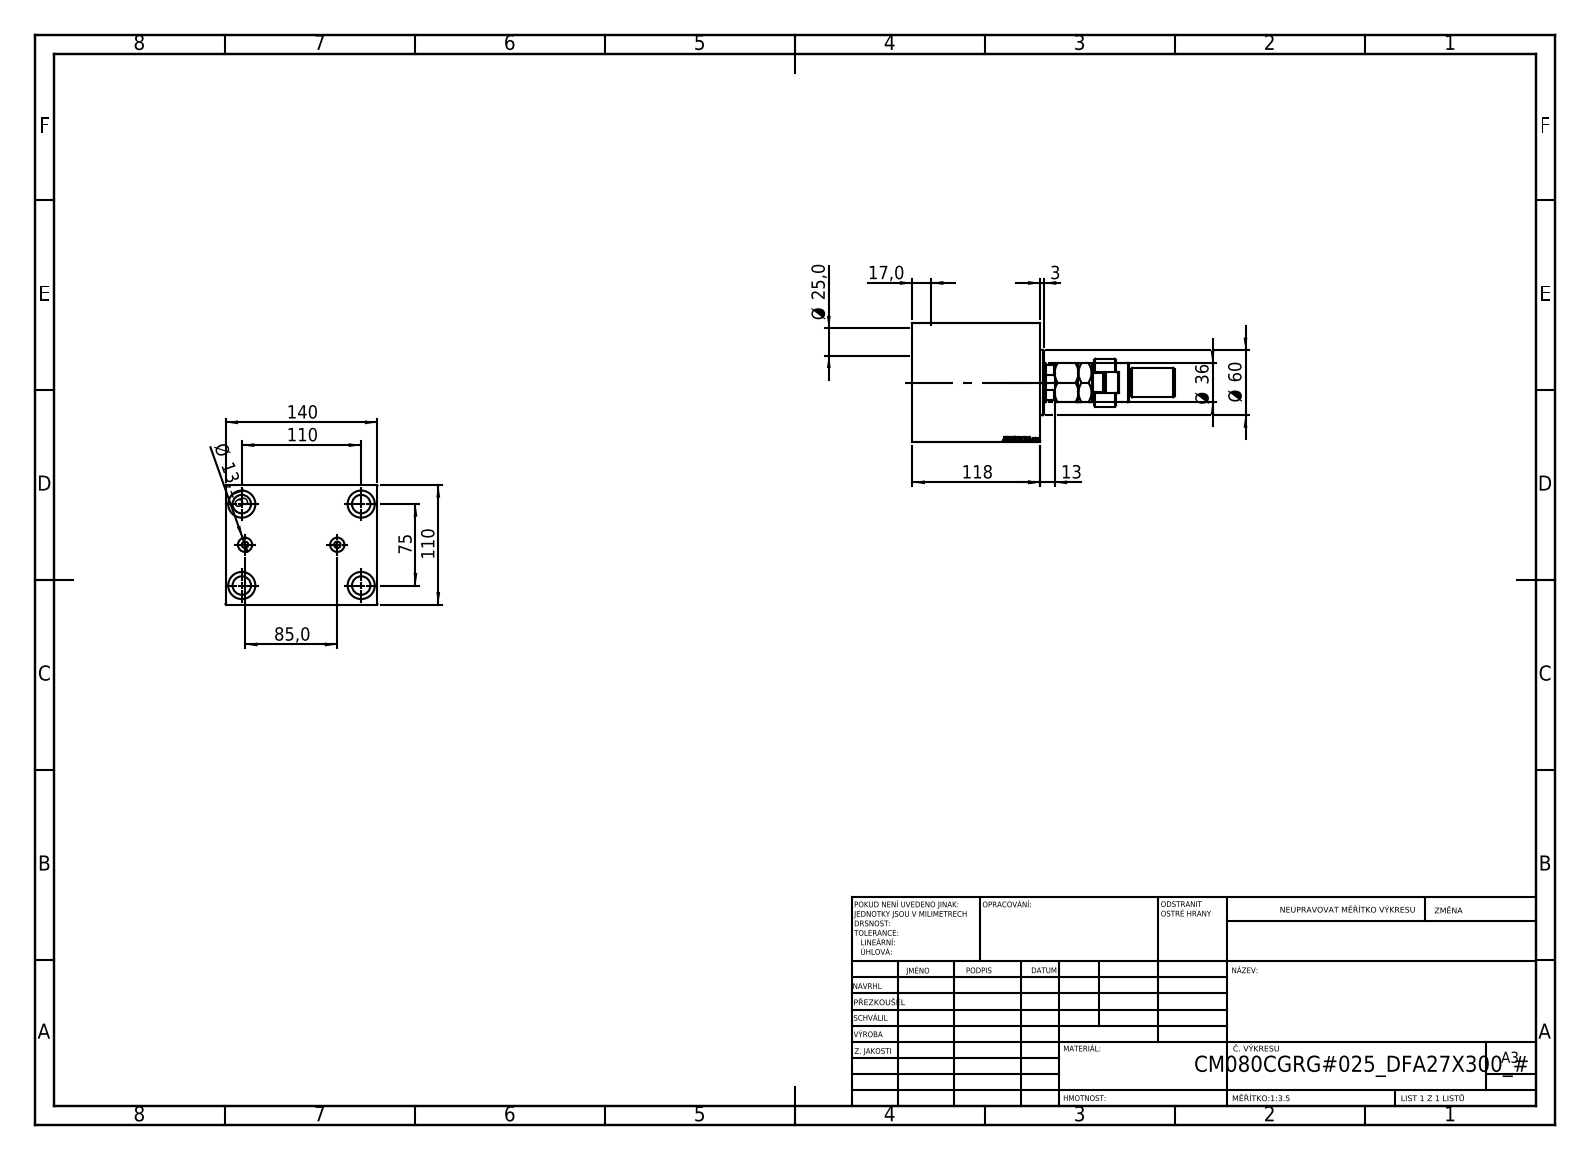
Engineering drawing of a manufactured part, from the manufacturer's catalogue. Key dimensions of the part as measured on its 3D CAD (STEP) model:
Part name (STEP PRODUCT): V450CM_C_Body; V450CM_VC_B; FEMALE_PART_FOR_DFA; MFA (+1 more)
STEP written by: SolidWorks 2019 (CONFIG_CONTROL_DESIGN)
Units: millimetres
Bodies: 5 solids, 945 faces (436 planar, 71 cylindrical, 438 other)
Overall size (bounding box): 241.5 × 140 × 110
Volume: 1 725 000 mm³ · Surface area: 195 676 mm²
Round holes (diameter × count): ⌀17 ×4, ⌀25 ×4, ⌀6 ×2, ⌀13.16 ×2, ⌀25.5 ×1, ⌀39.5 ×1, ⌀80 ×1, ⌀82 ×1, ⌀87 ×1
Round bosses / shafts (diameter × count): ⌀60 ×1, ⌀44 ×1, ⌀36 ×1, ⌀28 ×1, ⌀27 ×1, ⌀25 ×1, ⌀18 ×1
Partial cylindrical surfaces — rounded edges, fillets, slot ends (radius × count): R9.5 ×1, R15 ×1, R17.5 ×1
Main face-to-face distances: 110, 140, 51, 118, 67, 10, 21.6, 29.4, 96.4, 86.4
Hole centre spacings: 66.57, 37.62, 43.48, 75, 95.66, 110, 113.38, 133.14
